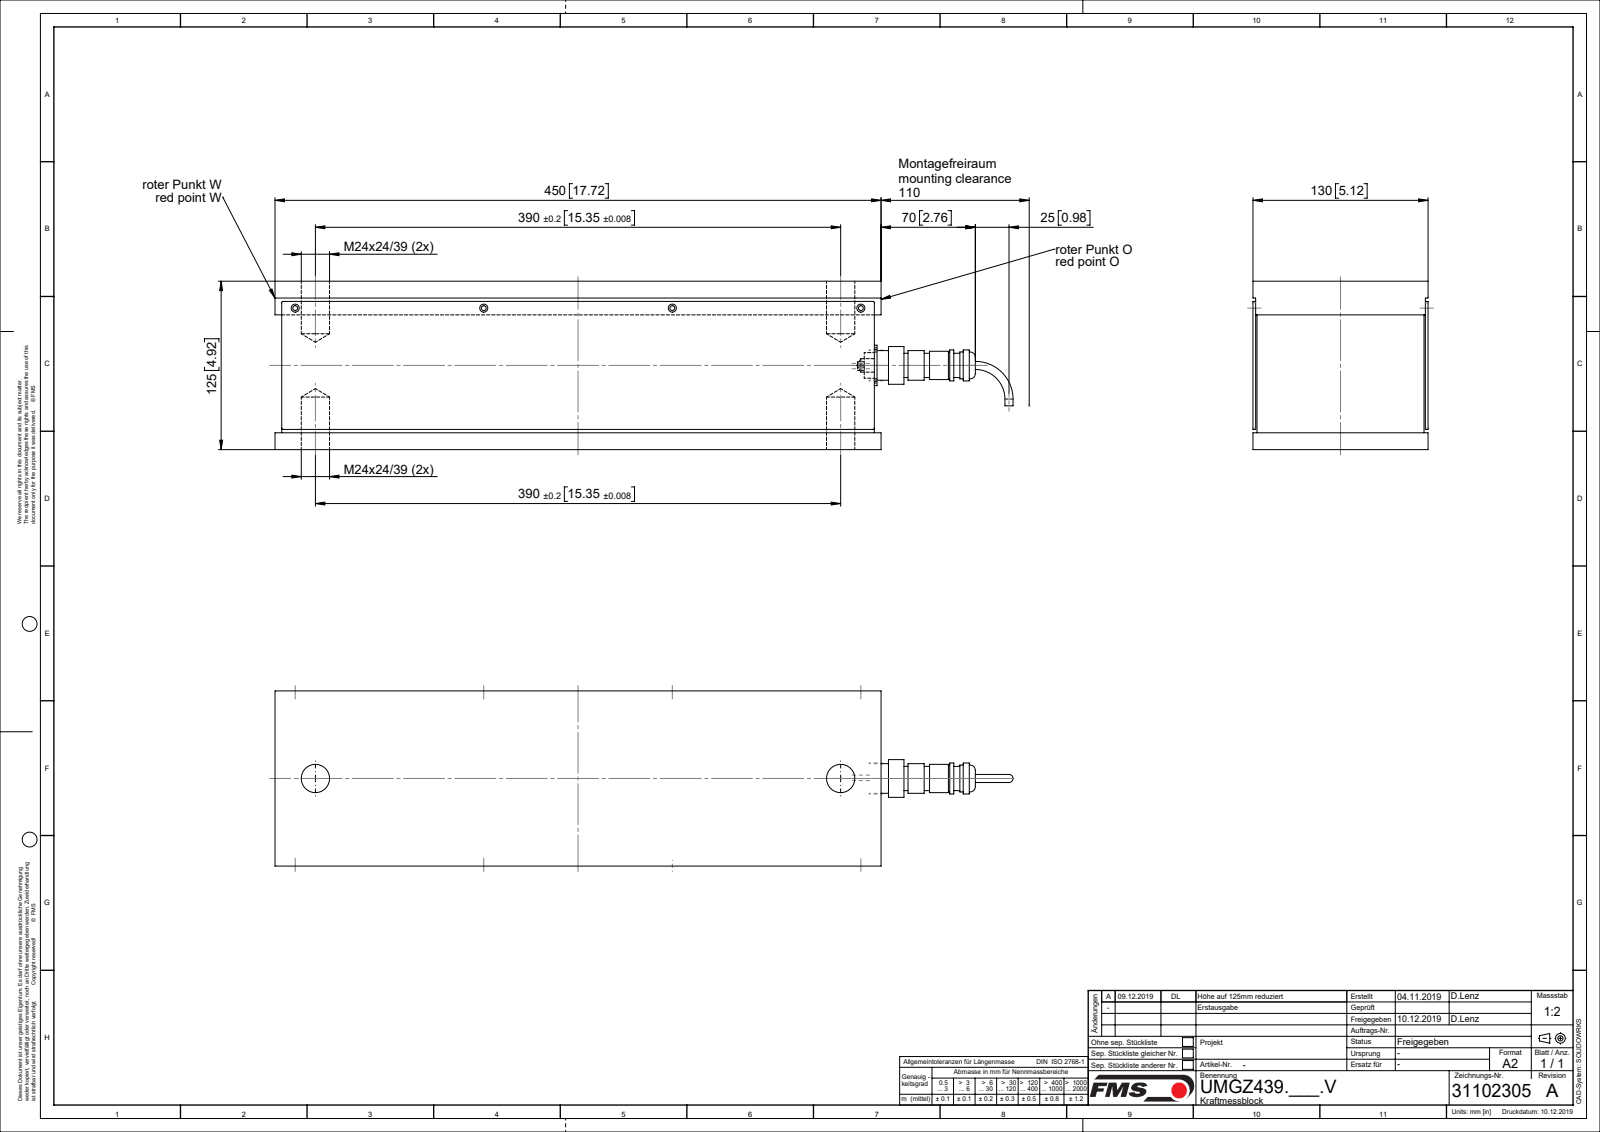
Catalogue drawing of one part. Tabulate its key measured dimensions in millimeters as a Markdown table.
| quantity | value |
| --- | --- |
| part name | 31102358_01; 51585_01; 31102305_A; 31101648_01 |
| STEP written by | SolidWorks 2018 (CONFIG_CONTROL_DESIGN) |
| units | millimeters |
| bodies | 4 solids, 186 faces (56 planar, 100 cylindrical, 30 other) |
| overall size | 548 × 130 × 125 |
| volume | 7 088 000 mm³ |
| surface area | 459 109 mm² |
| round holes (diameter × count) | 3.2 × 4, 3.6 × 4, 6 × 4, 21 × 2, 10 × 1 |
| round bosses / shafts (diameter × count) | 2.5 × 4, 28 × 1, 23 × 1, 22 × 1, 21 × 1, 20 × 1, 19 × 1, 18 × 1 |
| partial cylindrical surfaces (radius × count) | 1 × 4, 4 × 4 |
| main face-to-face distances | 125, 2, 128, 3, 1, 127, 130, 126, 124, 440 |
| hole center spacings | 16.26, 23, 140, 32.53, 280, 390, 420 |
